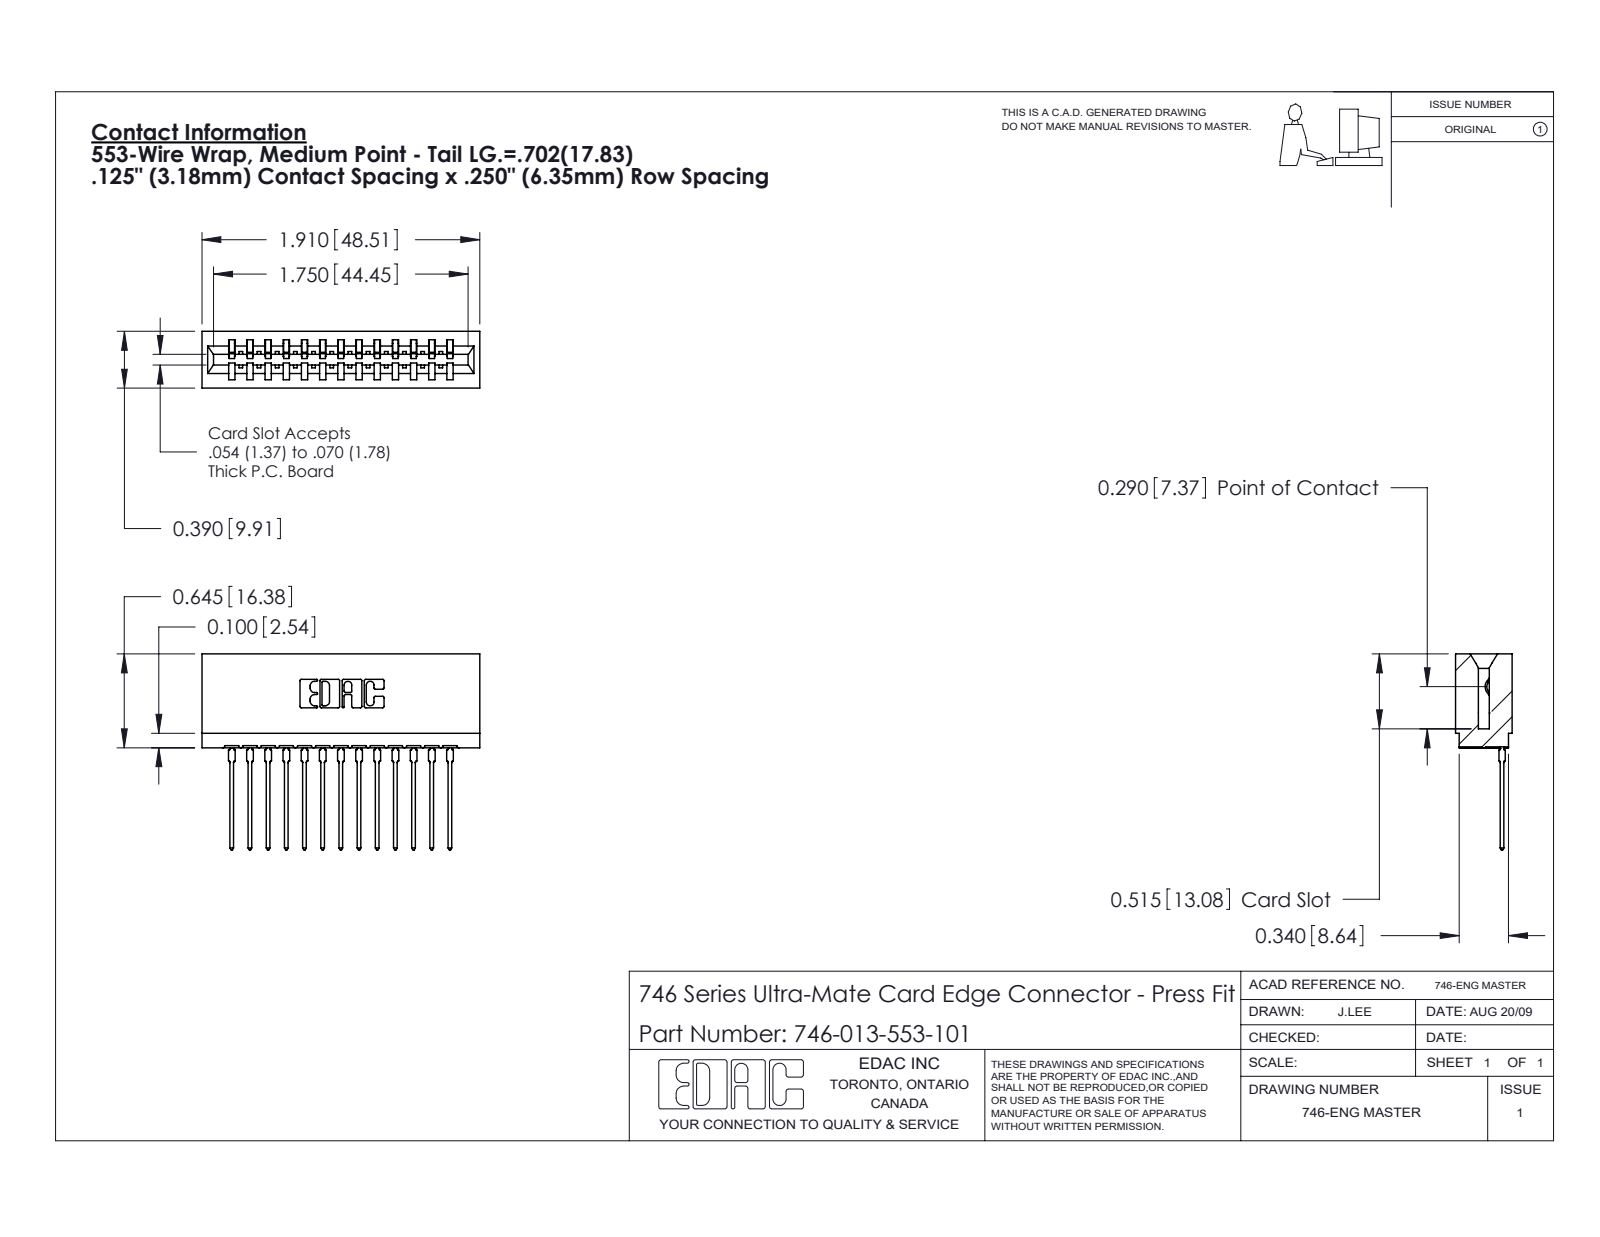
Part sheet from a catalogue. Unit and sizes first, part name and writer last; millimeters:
Units: millimetres
Overall size (bounding box): 48.5 × 34.2 × 9.9
Partial cylindrical surfaces — rounded edges, fillets, slot ends (radius × count): R0.5 ×26, R0.3 ×22, R0.4 ×14, R0.2 ×6, R0.8 ×6, R0.1 ×4, R0.3 ×4, R0.7 ×3
Main face-to-face distances: 6.4, 8.5, 1.4, 12.7, 9.9, 3.2, 2.1, 3.2, 1.1, 5.3
Volume: 5 310 mm³ · Surface area: 7 632 mm²
Bodies: 14 solids, 1501 faces (874 planar, 289 cylindrical, 338 other)
Part name (STEP PRODUCT): 746-292-001_553; 746 Part_.515 Slot Depth - 01; 746-013-553-101
STEP written by: SolidWorks 2020 (CONFIG_CONTROL_DESIGN)
